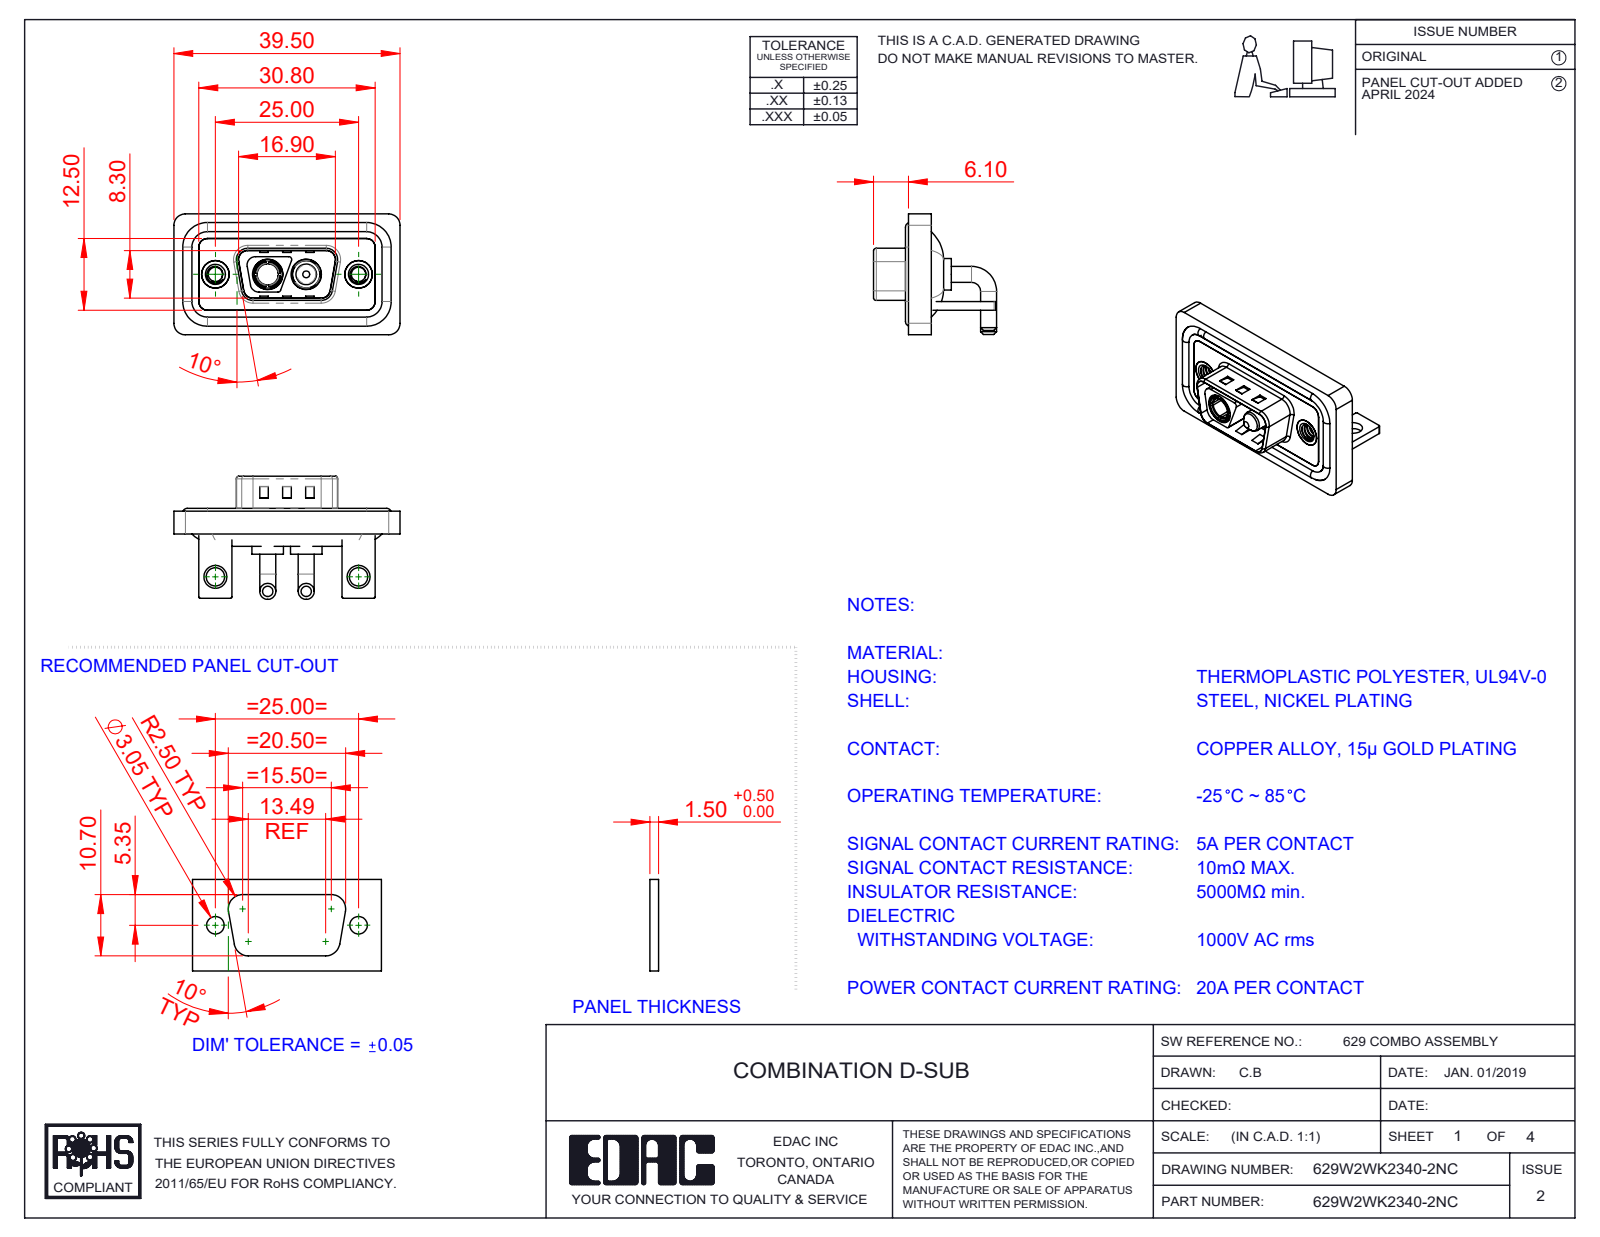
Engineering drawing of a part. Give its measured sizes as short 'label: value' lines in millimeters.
name: 629W2WK2340-2NC; 629Combo Housing_2WK2; 629Combo Shell Rear_09 Contacts; 629Combo Threaded Rivet_B (+5 more)
written by: SolidWorks 2023 (CONFIG_CONTROL_DESIGN)
unit: mm
bodies: 13 solids, 580 faces (209 planar, 249 cylindrical, 122 other)
size: 39.5 × 21.5 × 21.1
volume: 4 954 mm³; area: 8 120 mm²
holes: 2× ⌀2.5, 2× ⌀3.2, 2× ⌀4, 2× ⌀4.8, 2× ⌀4.85, 2× ⌀5, 2× ⌀5.3, 1× ⌀3.7
bosses: 4× ⌀2.8, 4× ⌀1.6, 2× ⌀5.5, 2× ⌀5.2, 2× ⌀4.9, 2× ⌀4.75, 2× ⌀3.75, 1× ⌀4.96
rounds: 20× R1.5, 19× R2, 16× R0.25, 11× R0.5, 8× R1.6, 4× R0.6, 4× R0.65, 4× R0.9
face distances: 0.4, 1.5, 2.9, 0.8, 1.1, 1.2, 2.1, 1.6, 3.7, 2.5
hole spacings: 9.14, 15.86, 25, 6.72
